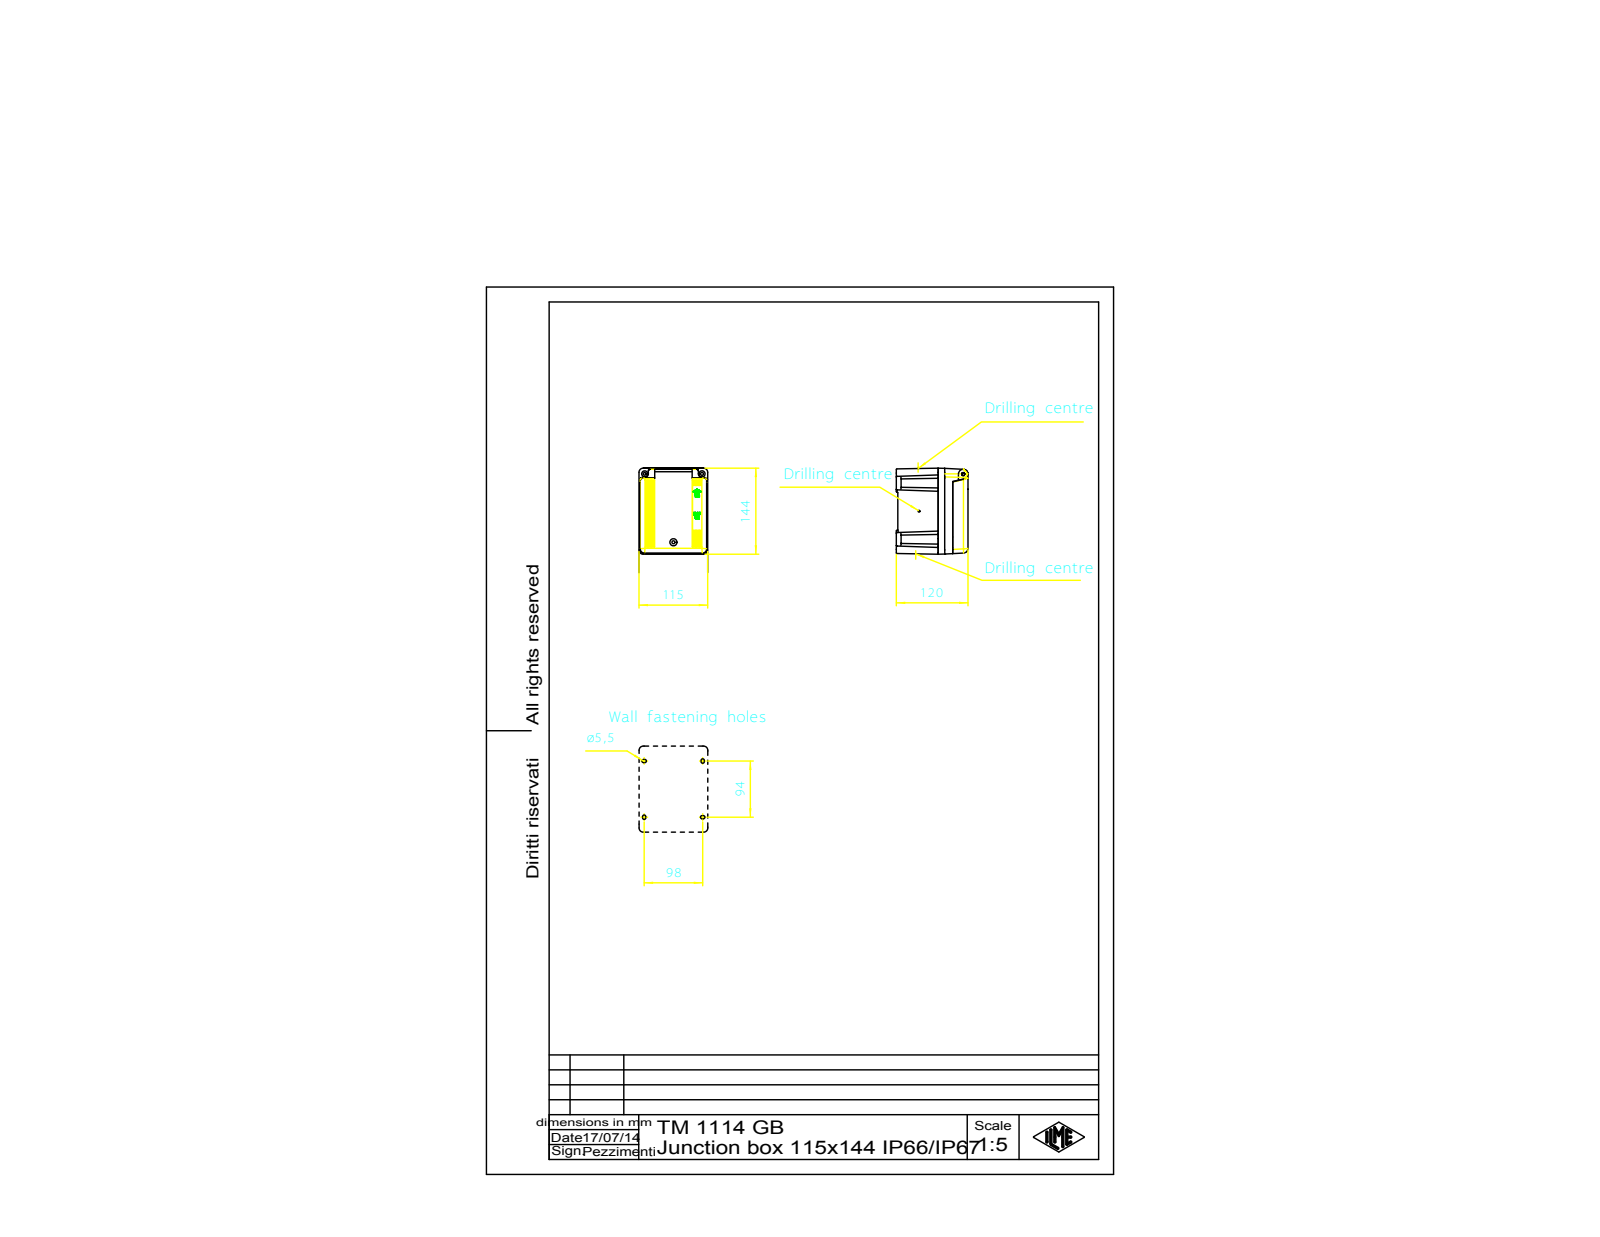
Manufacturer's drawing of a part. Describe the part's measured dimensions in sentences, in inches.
The part is named "SCATOLA_1114; CALOTTA_1114; SPORTELLO_1114; TM_1114_GB". Its 3-D file was written by "Creo Elements/Direct Modeling 20.5B 27-May-2023 (C) Parametric Technology GmbH (AUTOMOTIVE_DESIGN)". It is 3 solids with 1208 faces: 939 planar, 172 cylindrical and 97 other. Overall it measures 5.669 by 4.74 by 4.528 inches. Its volume is 45.47 cubic inches and its surface area 340.7 square inches. Round holes: 4 of diameter 0.11, 4 of diameter 0.205, 1 of diameter 0.197, 1 of diameter 0.213. Round bosses or shafts: 5 of diameter 0.335, 5 of diameter 0.197, 2 of diameter 0.264, 2 of diameter 0.157. Partial cylindrical surfaces (rounded edges, fillets, slot ends): 16 of radius 0.138, 12 of radius 0.276, 11 of radius 0.01, 8 of radius 0.106, 8 of radius 0.118, 8 of radius 0.315, 8 of radius 0.374, 7 of radius 0.02. The main face-to-face distances are 0.197, 4.429, 2.657, 1.772, 3.622, 3.425, 4.626, 1.004, 0.157, 1.969. The hole center spacings are 2.489, 4.202, 0.922, 1.9, 1.935, 2.547, 3.127, 3.282.
